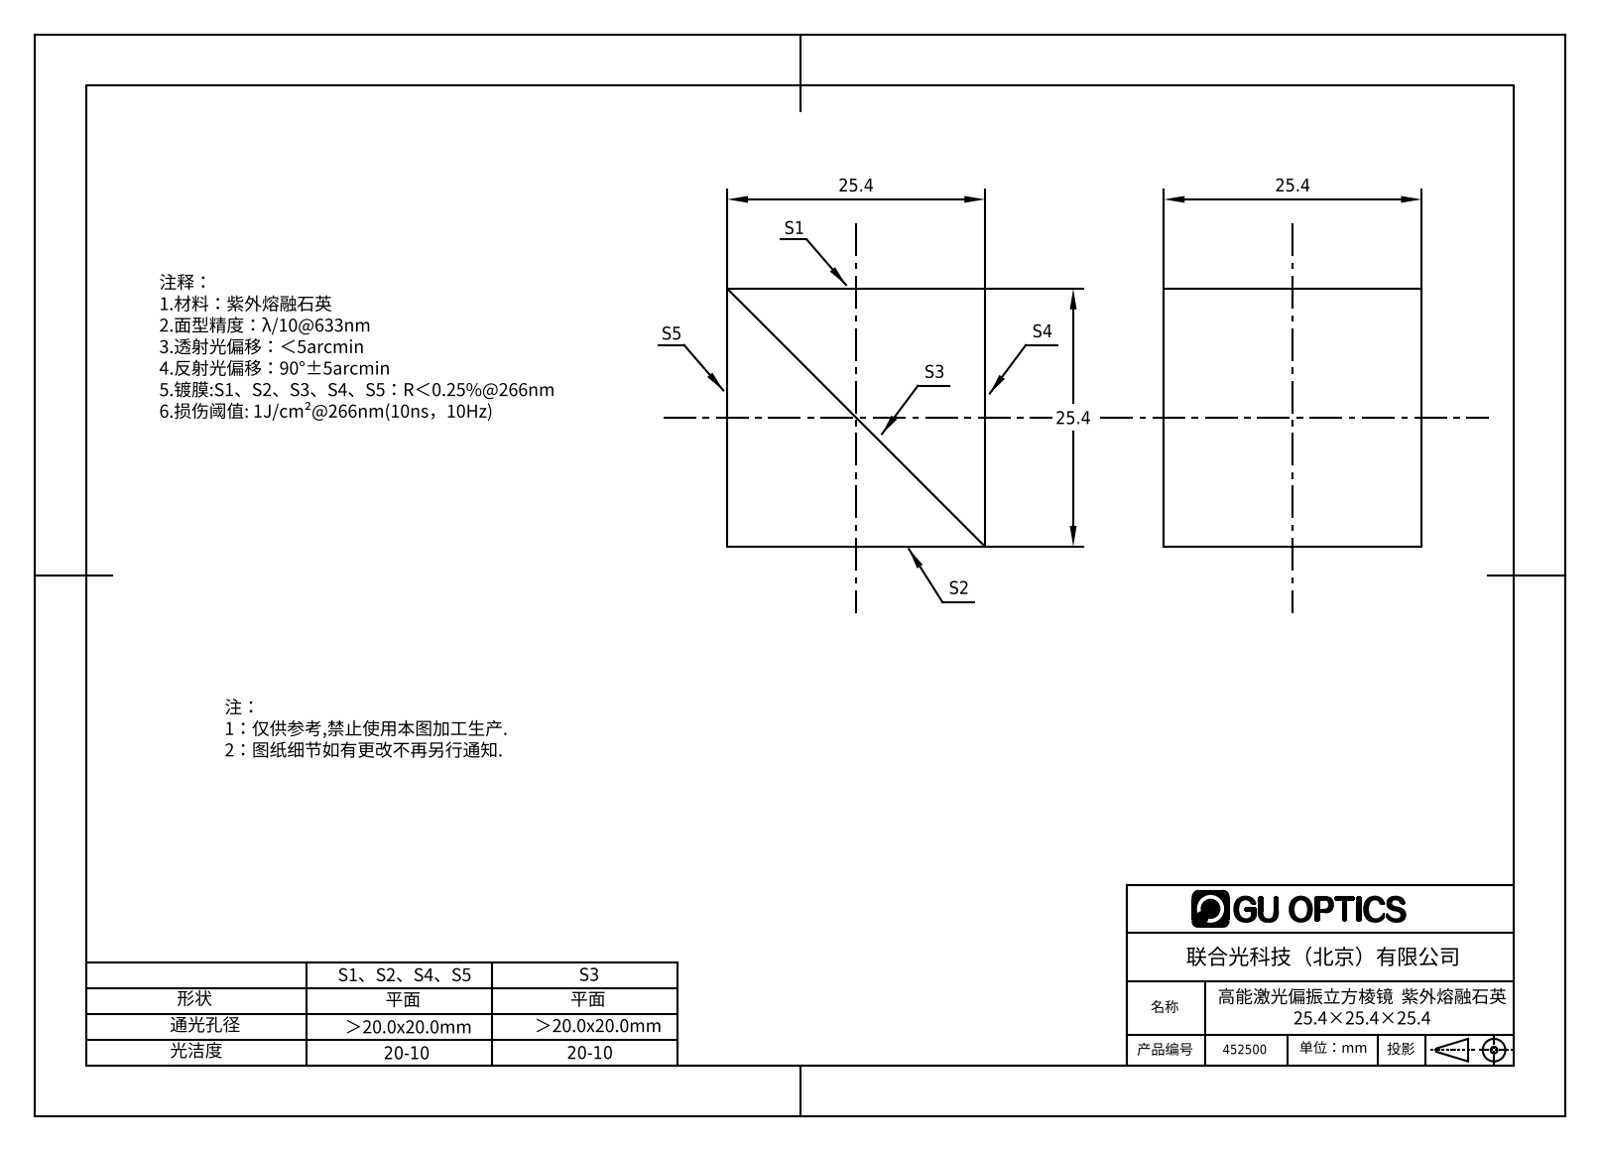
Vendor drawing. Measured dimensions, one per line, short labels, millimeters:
name: 372010
written by: SolidWorks 2020 (CONFIG_CONTROL_DESIGN)
unit: mm
bodies: 2 solids, 10 faces (10 planar, 0 cylindrical, 0 other)
size: 25.4 × 25.4 × 25.4
volume: 16 387 mm³; area: 5 696 mm²
face distances: 25.4
